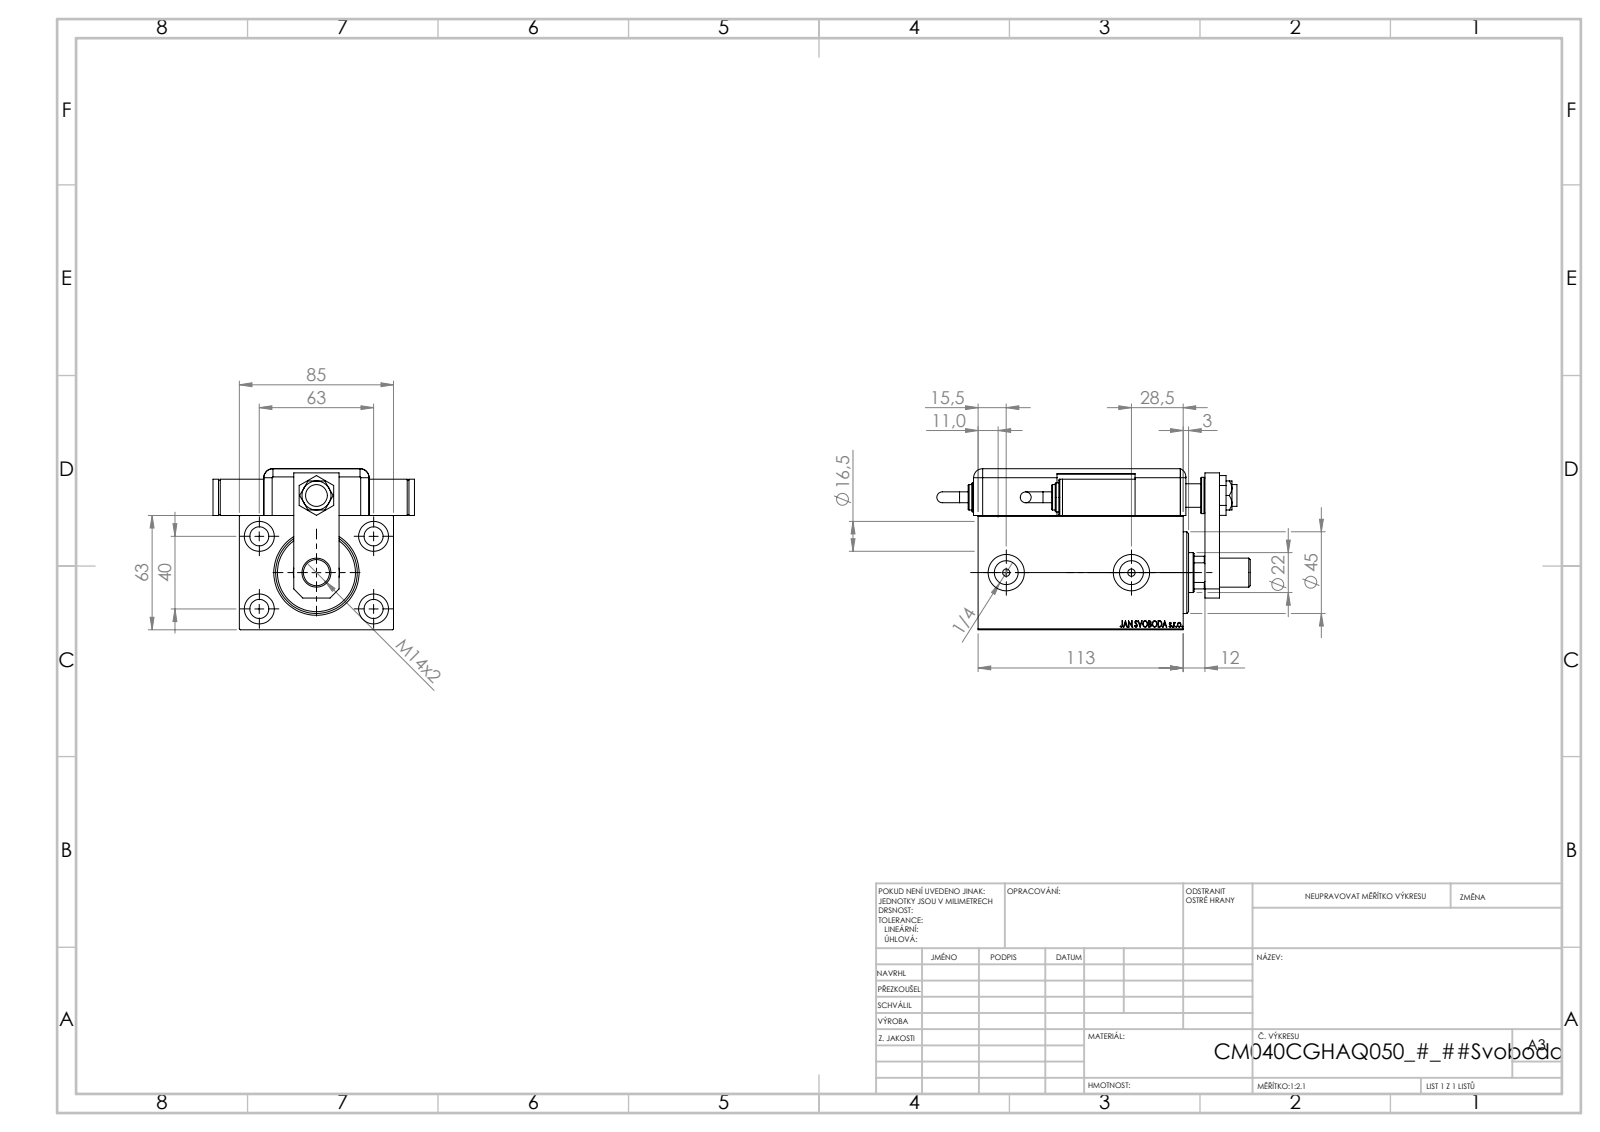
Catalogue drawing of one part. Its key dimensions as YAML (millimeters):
part_name: "ZARAZKA_Q; SWITCH DIM A_G; V450CM_VC_B; V450CM_C_Body (+7 more)"
step_written_by: "SolidWorks 2019 (CONFIG_CONTROL_DESIGN)"
units: millimeters
bodies: {solids: 14, faces: 1260, planar: 618, cylindrical: 119, other: 523}
overall_size: [172.76, 111, 88.8]
volume: 662191
surface_area: 151279
round_holes:
  - {diameter: 4, count: 4}
  - {diameter: 10.5, count: 4}
  - {diameter: 16.5, count: 4}
  - {diameter: 8, count: 2}
  - {diameter: 13.16, count: 2}
  - {diameter: 14, count: 2}
  - {diameter: 20, count: 2}
  - {diameter: 12, count: 1}
  - {diameter: 12.5, count: 1}
  - {diameter: 13, count: 1}
  - {diameter: 22, count: 1}
  - {diameter: 25.5, count: 1}
round_bosses_or_shafts:
  - {diameter: 20, count: 3}
  - {diameter: 16, count: 3}
  - {diameter: 14, count: 3}
  - {diameter: 6, count: 2}
partial_cylinders:
  - {radius: 5, count: 9}
  - {radius: 10, count: 1}
  - {radius: 10.5, count: 1}
face_to_face_distances: [3, 63, 13.5, 85, 12, 25.8, 88.8, 113, 20, 83]
hole_center_spacings: [37.31, 36.79, 37.86, 38.71, 40, 63, 69.99, 74.63]
